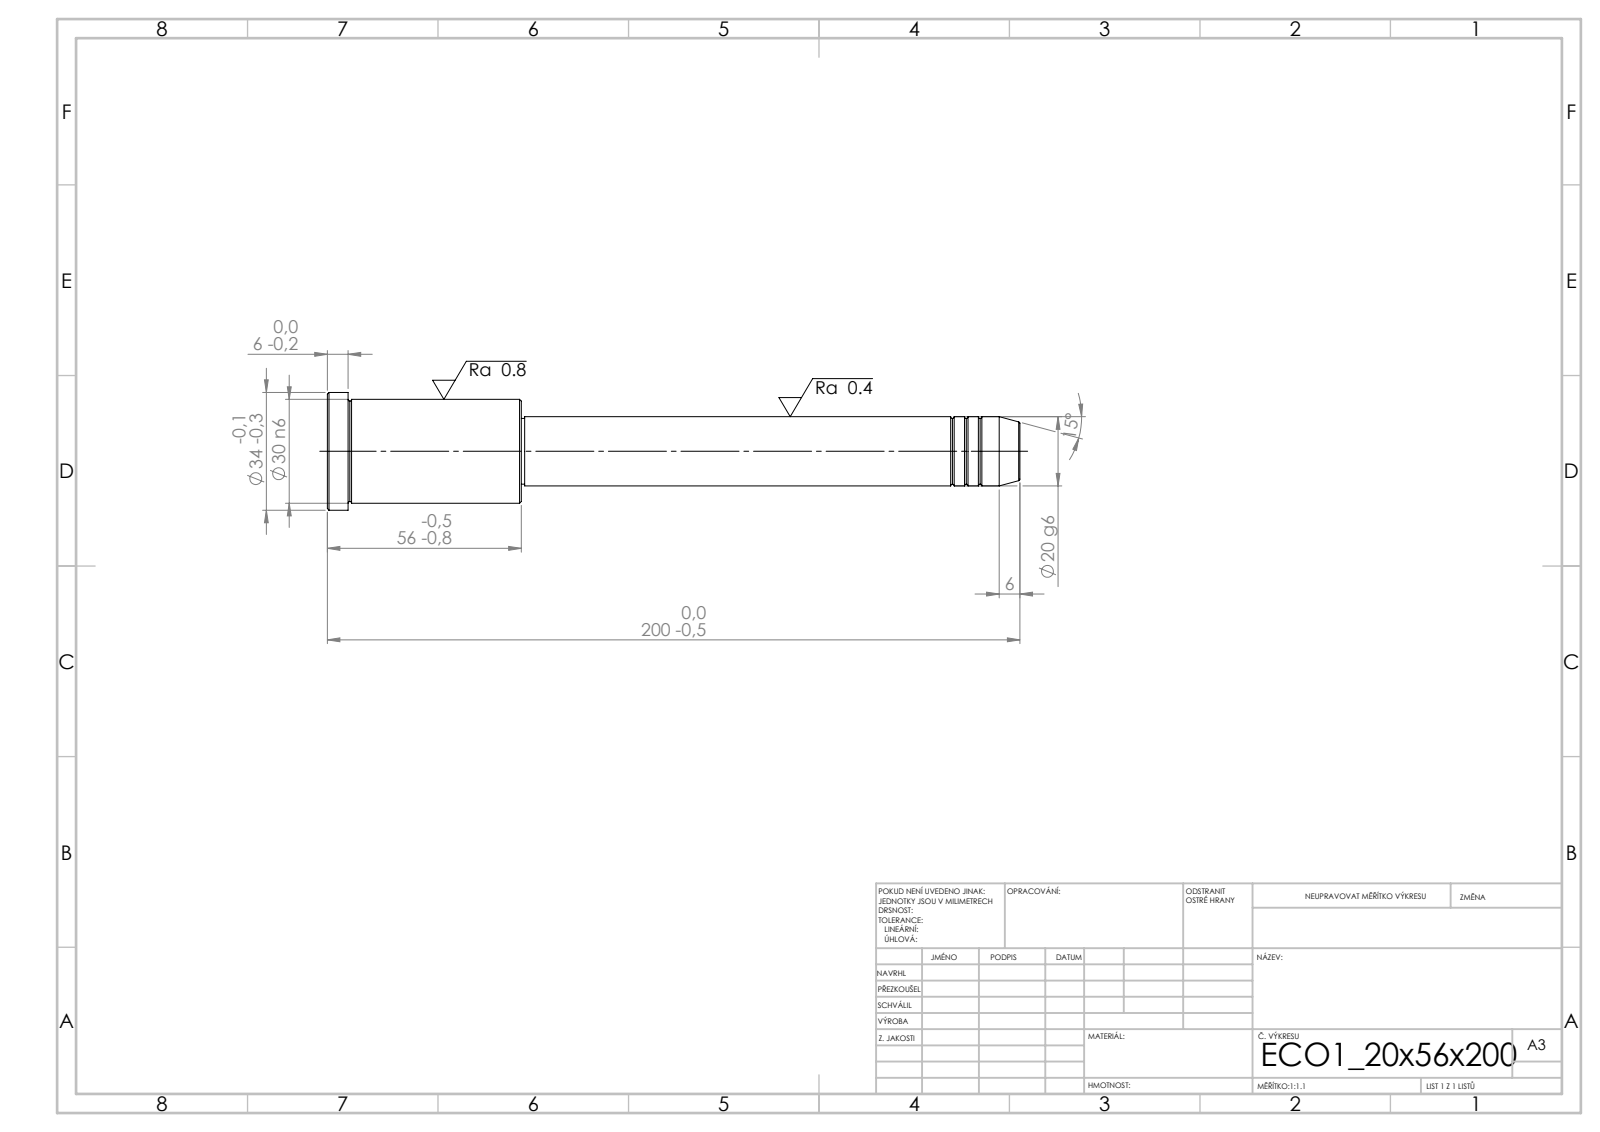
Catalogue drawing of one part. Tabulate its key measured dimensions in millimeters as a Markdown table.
| quantity | value |
| --- | --- |
| STEP written by | SolidWorks 2019 (CONFIG_CONTROL_DESIGN) |
| units | millimeters |
| bodies | 1 solid, 43 faces (5 planar, 14 cylindrical, 24 other) |
| overall size | 200 × 34 × 34 |
| volume | 85 577 mm³ |
| surface area | 16 247 mm² |
| round bosses / shafts (diameter × count) | 34 × 1, 30 × 1, 20 × 1, 19 × 1 |
| main face-to-face distances | 56, 144, 200, 194, 50, 6, 143, 1, 51, 57 |
